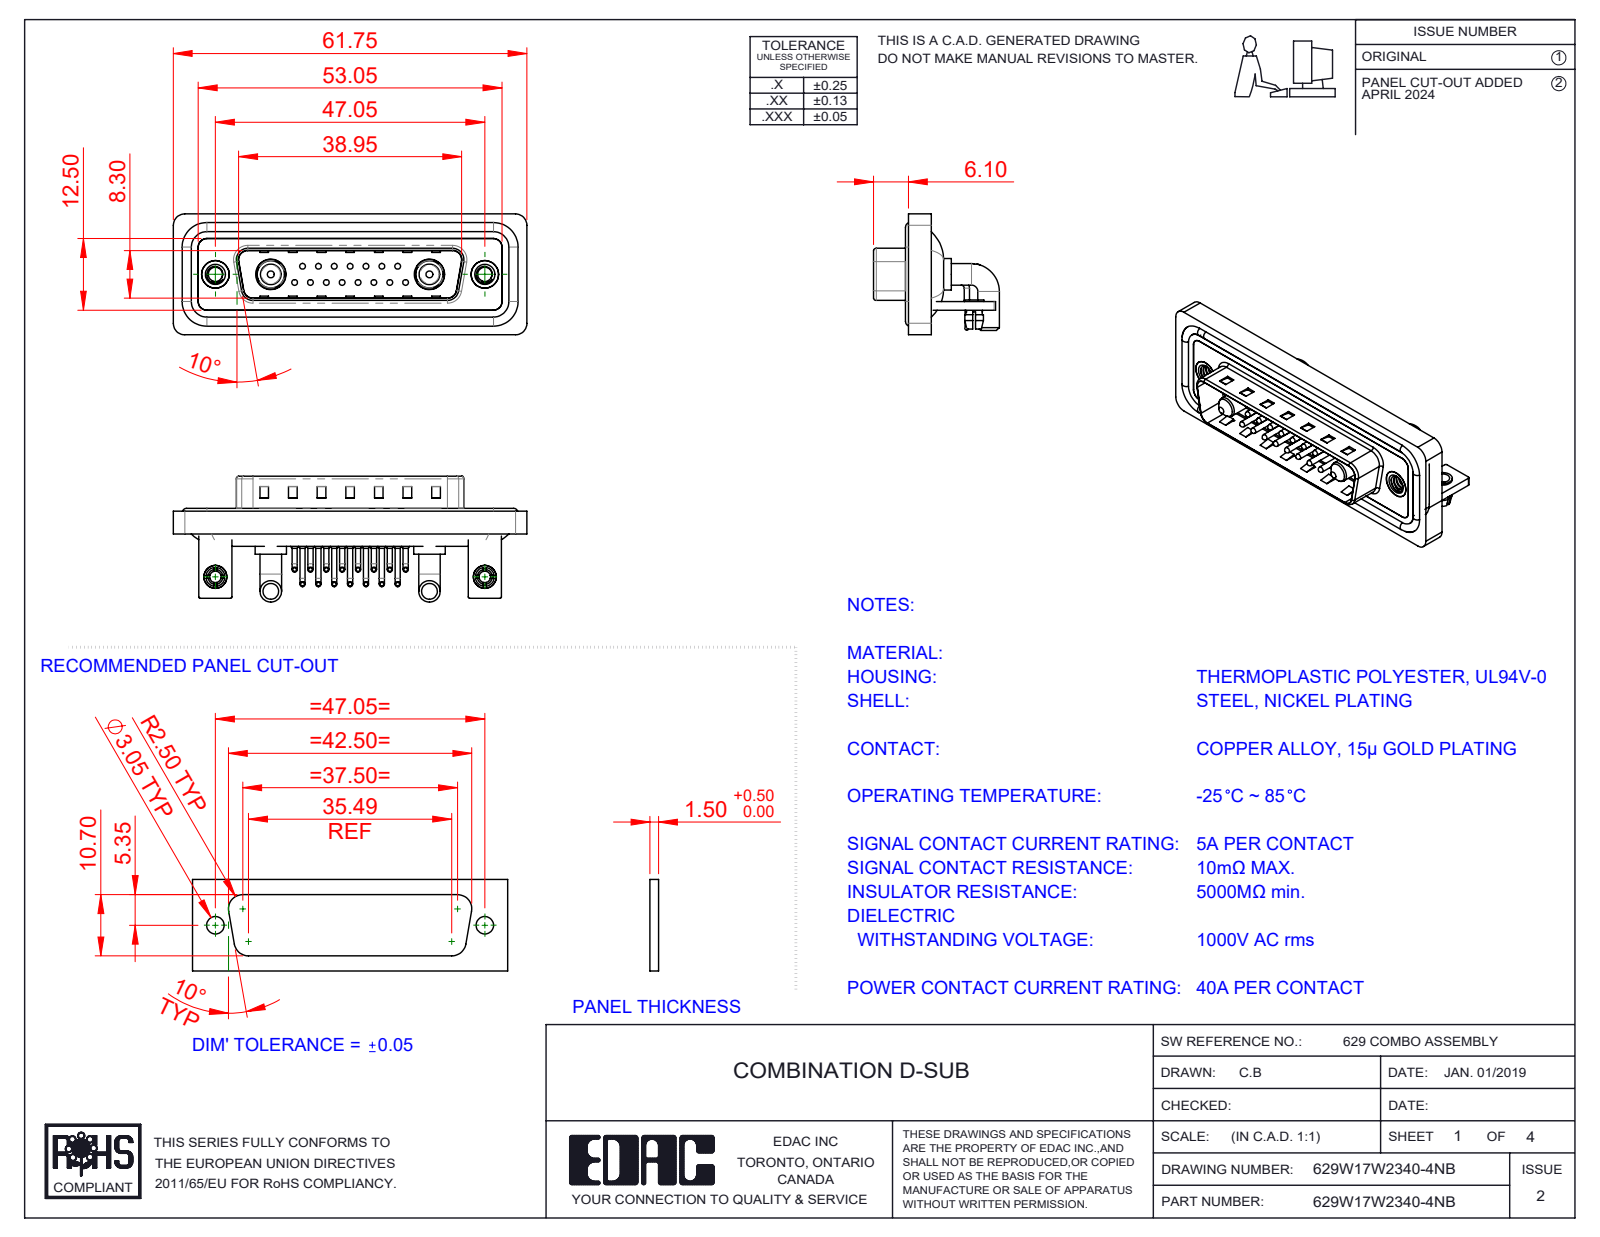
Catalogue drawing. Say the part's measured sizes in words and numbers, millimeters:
The part is named "629Combo Shell Front_25 Contacts; 629Combo Board Lock; 629Combo Contact Row 1; 629Combo Contact Row 2 (+7 more)". Its 3-D file was written by "SolidWorks 2023 (CONFIG_CONTROL_DESIGN)". It is 30 solids with 2349 faces: 1257 planar, 820 cylindrical and 272 other. Overall it measures 61.75 by 21.98 by 21.1 millimeters. Its volume is 7 966 cubic millimeters and its surface area 13 487 square millimeters. Round holes: 17 of diameter 2, 15 of diameter 0.75, 15 of diameter 1.6, 4 of diameter 2.5, 2 of diameter 3.2, 2 of diameter 4, 2 of diameter 4.8, 2 of diameter 4.85, 2 of diameter 5, 2 of diameter 5.3. Round bosses or shafts: 30 of diameter 0.9, 15 of diameter 1.5, 15 of diameter 1, 15 of diameter 0.65, 4 of diameter 3.75, 4 of diameter 1.6, 2 of diameter 5.5, 2 of diameter 5.2. Partial cylindrical surfaces (rounded edges, fillets, slot ends): 19 of radius 2, 18 of radius 1.5, 16 of radius 0.25, 15 of radius 1.01, 9 of radius 0.5, 8 of radius 1.6, 4 of radius 0.6, 4 of radius 0.65. The main face-to-face distances are 0.4, 0.8, 2.1, 1.5, 2.9, 1.1, 4.1, 1.6, 4.5, 3.7. The hole center spacings are 3.16, 2.77, 5.54, 8.31, 5.04, 7.49, 11.08, 5.03.
